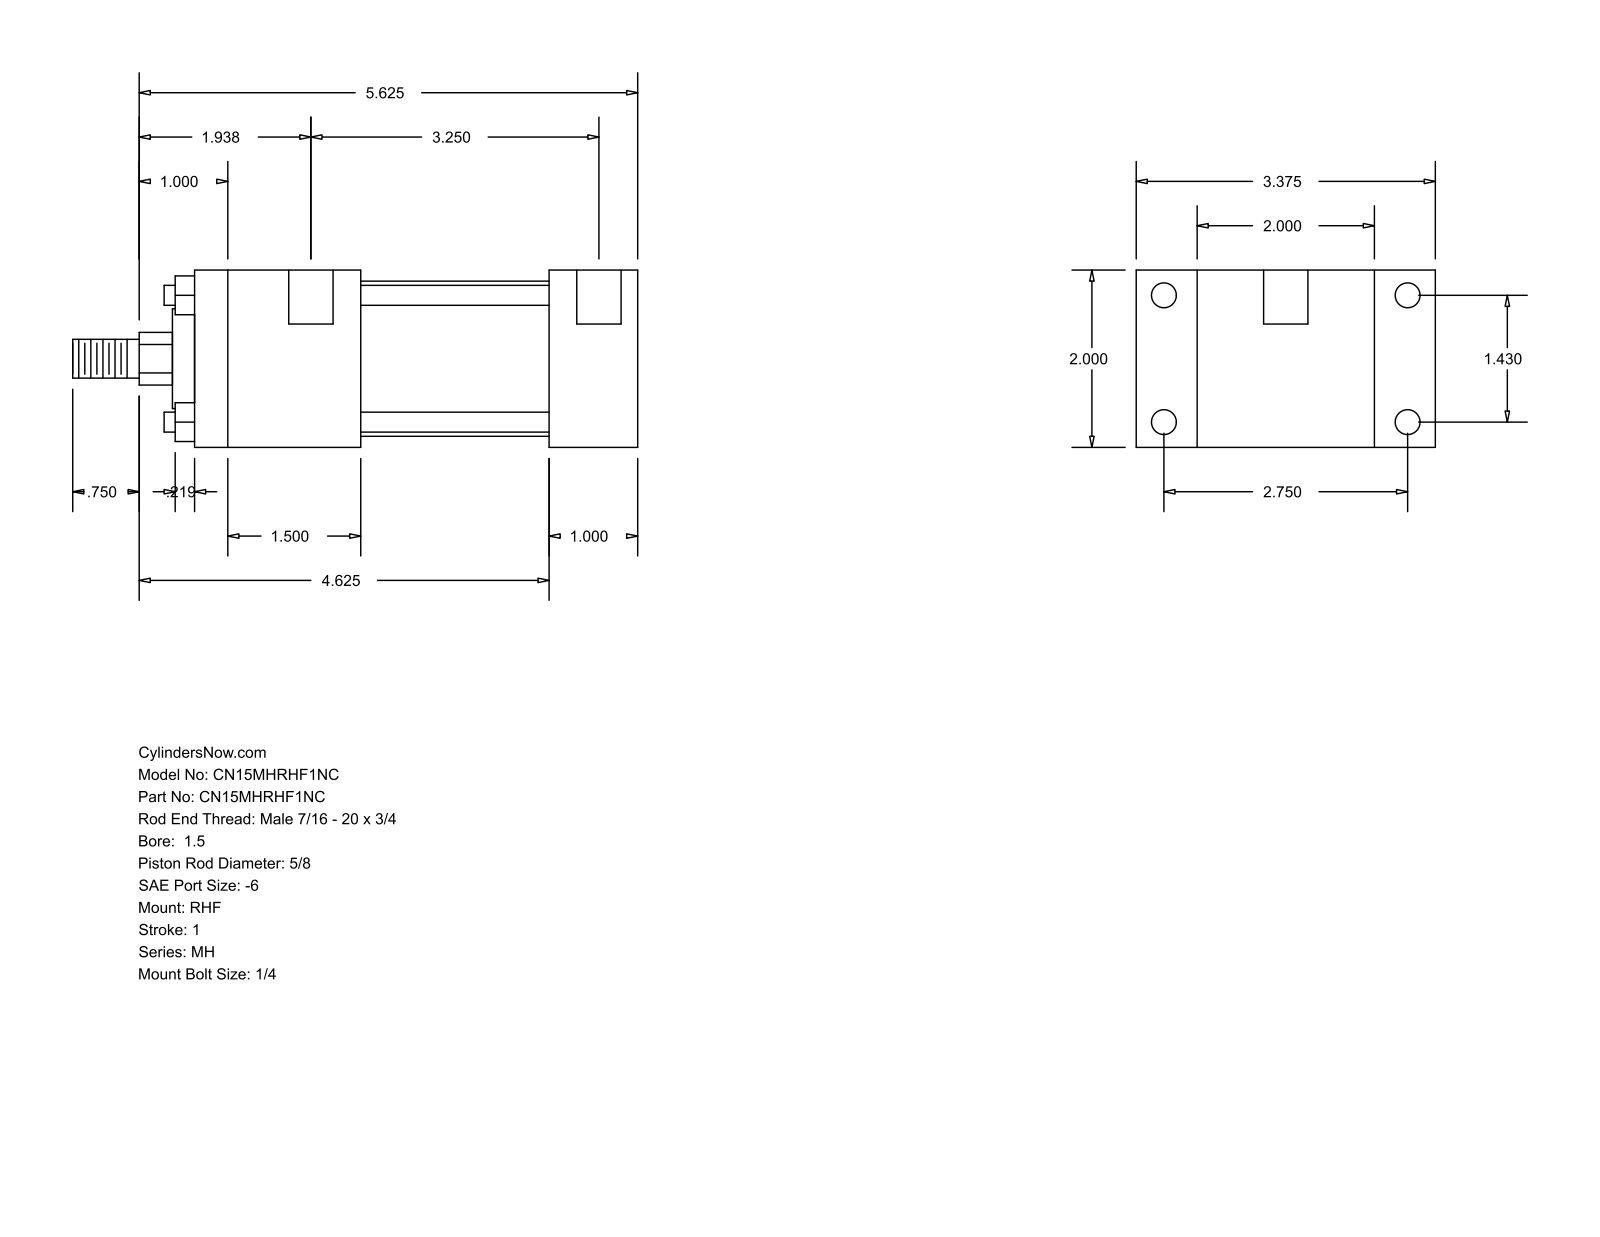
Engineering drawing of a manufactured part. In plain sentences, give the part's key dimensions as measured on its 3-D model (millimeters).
The part is named "MH_RHF__0150_0.625". Its 3-D file was written by "GSSL Pune (CONFIG_CONTROL_DESIGN)". It is 0 solids with 88 faces: 60 planar, 28 cylindrical and 0 other. Overall it measures 161.93 by 85.72 by 50.8 millimeters. Round holes: 4 of diameter 5.56, 4 of diameter 7.14, 2 of diameter 12.7. Round bosses or shafts: 4 of diameter 5.71, 1 of diameter 44.45, 1 of diameter 28.57, 1 of diameter 15.88, 1 of diameter 11.11. Partial cylindrical surfaces (rounded edges, fillets, slot ends): 1 of radius 7.54. The main face-to-face distances are 50.8, 17.46, 68.26, 25.41, 101.59, 127, 53.97, 85.72, 47.62, 79.38. The hole center spacings are 36.32, 69.84, 78.72, 85.72, 3.17, 82.55.
